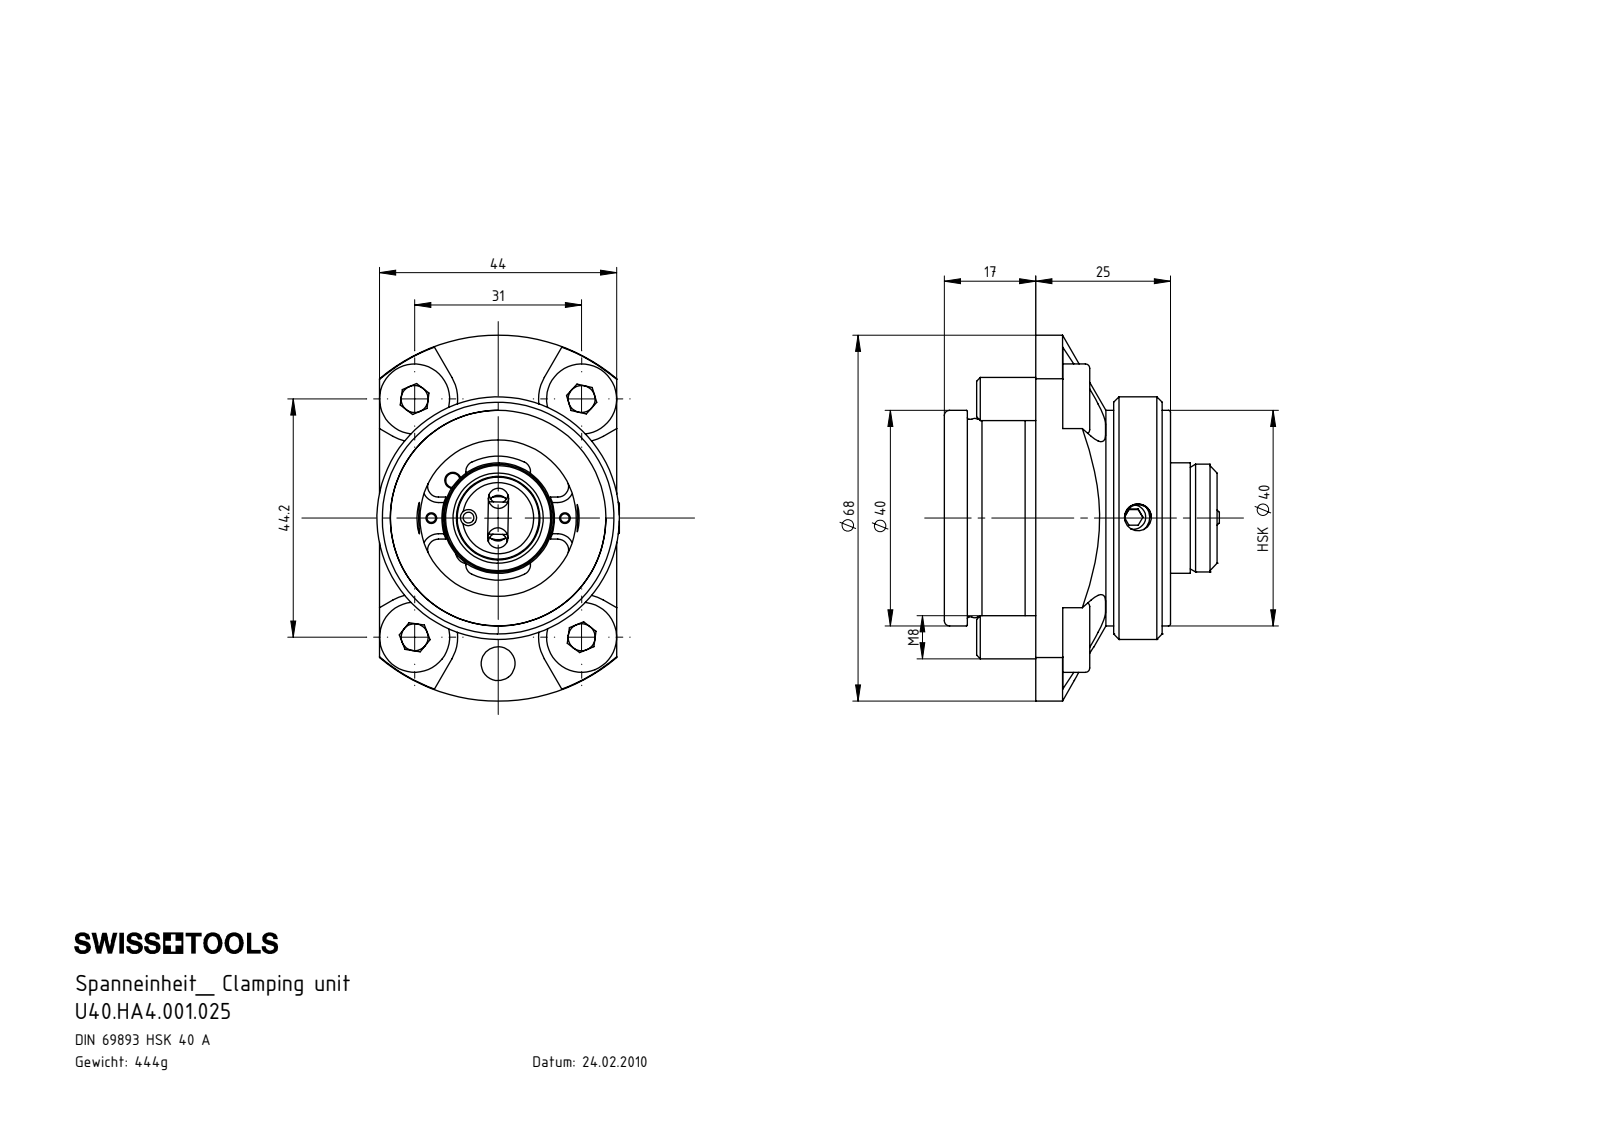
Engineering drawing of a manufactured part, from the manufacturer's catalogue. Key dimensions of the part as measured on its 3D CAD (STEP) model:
Part name (STEP PRODUCT): U40.HA4.001.025; ISO 13337 - 3 x 14_PreviewCfg; U40-ER1.010.012_A; U40-HA4.001.025_E (+8 more)
STEP written by: SolidWorks 2017 (AUTOMOTIVE_DESIGN)
Units: millimetres
Bodies: 18 solids, 479 faces (220 planar, 143 cylindrical, 116 other)
Overall size (bounding box): 77 × 67.9 × 45
Volume: 98 894 mm³ · Surface area: 42 660 mm²
Round holes (diameter × count): ⌀9 ×4, ⌀1.6 ×2, ⌀3 ×2, ⌀3.5 ×2, ⌀3.75 ×2, ⌀5 ×2, ⌀2.4 ×1, ⌀4.2 ×1, ⌀4.6 ×1, ⌀6 ×1, ⌀6.3 ×1, ⌀8 ×1
Round bosses / shafts (diameter × count): ⌀13 ×4, ⌀8 ×4, ⌀45 ×1, ⌀40 ×1, ⌀39.5 ×1, ⌀36.65 ×1, ⌀34.75 ×1, ⌀33 ×1
Partial cylindrical surfaces — rounded edges, fillets, slot ends (radius × count): R1 ×8, R5 ×8, R0.9 ×6, R1.88 ×4, R1.95 ×4, R2 ×4, R4.5 ×4, R8 ×4
Main face-to-face distances: 5, 35, 20, 17, 77, 60, 42, 25, 22, 55
Hole centre spacings: 22.32, 26.99, 35.59, 3.67, 6.61, 12.4, 12.89, 12.97
